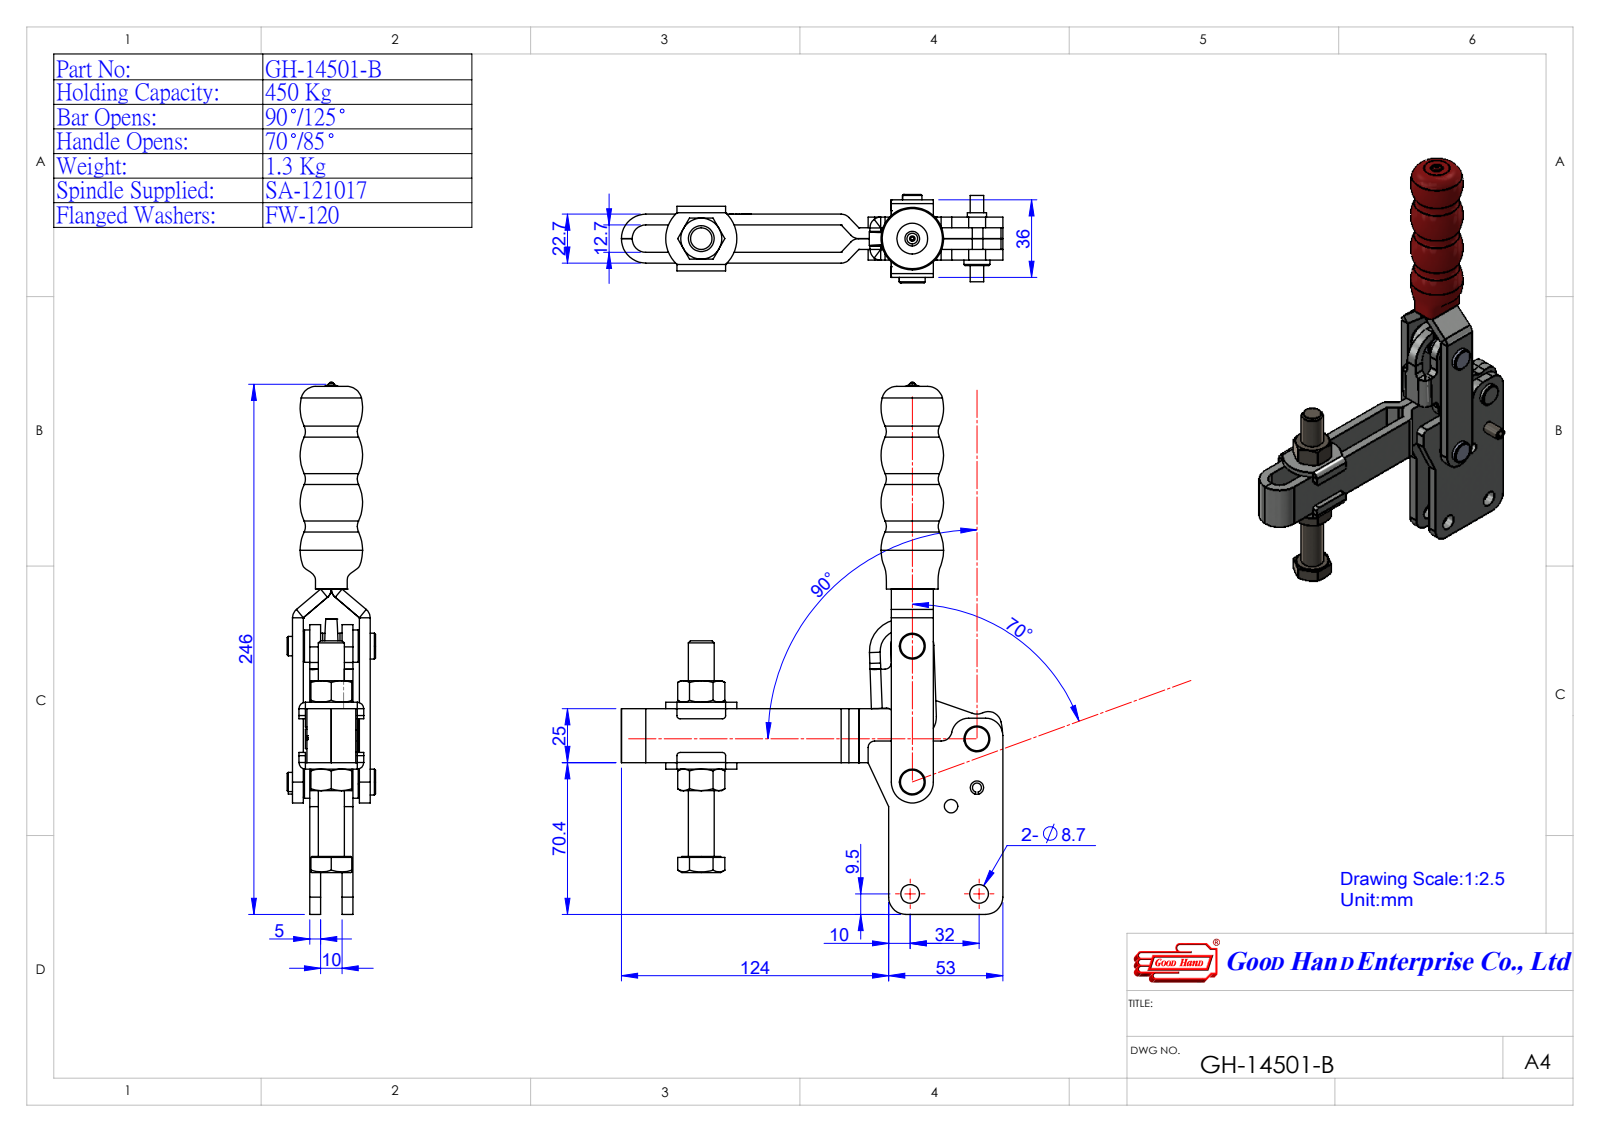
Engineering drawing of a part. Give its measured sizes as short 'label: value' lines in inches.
name: Group5^GH-14501-B(簡化)-1; Group4^GH-14501-B(簡化)-1; Group6^GH-14501-B(簡化)-1; GH-14501-B(簡化)-1 (+3 more)
written by: SolidWorks 2016 (AUTOMOTIVE_DESIGN)
unit: in
bodies: 7 solids, 658 faces (292 planar, 173 cylindrical, 193 other)
size: 9.721 × 6.969 × 1.614
volume: 12.46 in³; area: 124.5 in²
holes: 4× ⌀0.276, 2× ⌀0.343, 1× ⌀0.075, 1× ⌀0.236, 1× ⌀0.402, 1× ⌀0.472, 1× ⌀0.512
bosses: 4× ⌀0.394, 2× ⌀0.512, 2× ⌀0.354, 2× ⌀0.352, 1× ⌀0.709, 1× ⌀0.236, 1× ⌀0.072
rounds: 10× R0.197, 4× R0.059, 4× R0.119, 3× R0.029, 3× R0.03, 3× R0.315, 2× R0.118, 2× R0.394
face distances: 0.197, 0.591, 0.053, 0.644, 0.394, 0.787, 0.906, 0.315, 0.262, 0.959
hole spacings: 0.835, 1.183, 1.202, 1.26, 1.299, 1.316, 1.42, 1.682
